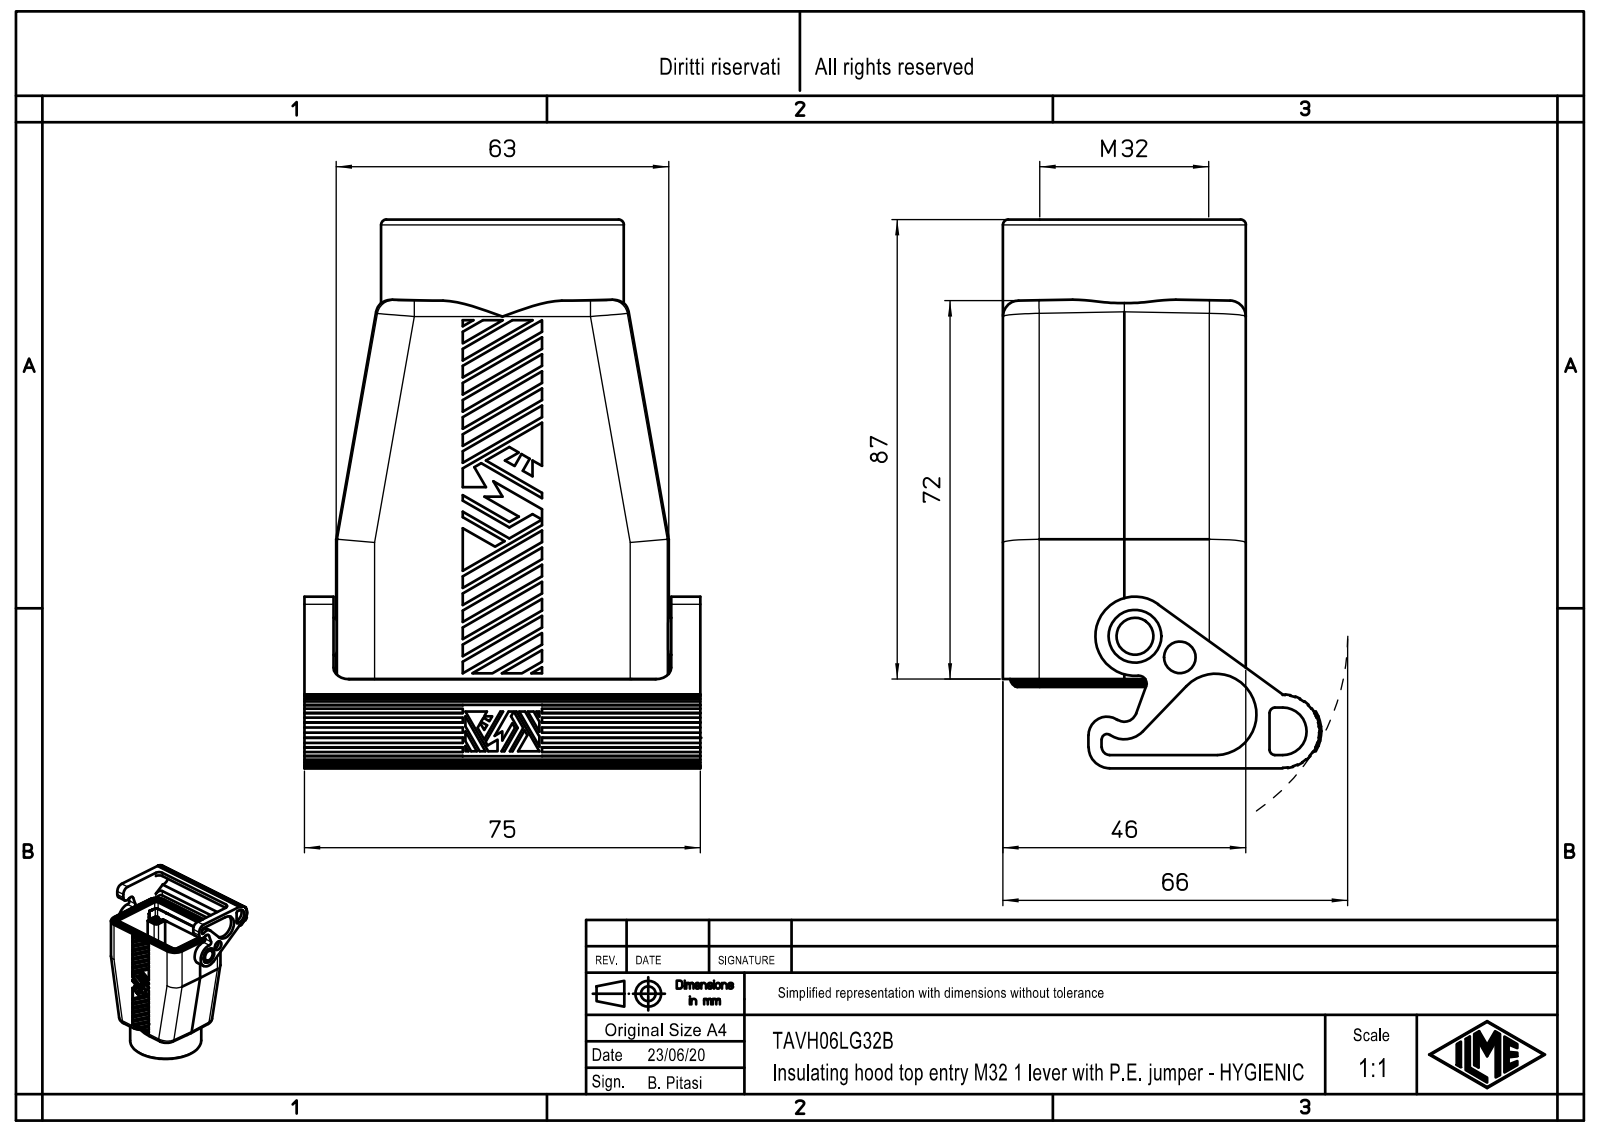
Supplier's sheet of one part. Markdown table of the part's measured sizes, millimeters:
| quantity | value |
| --- | --- |
| part name | TAVH06LG32B |
| STEP written by | Creo Elements/Direct Modeling 20.1B 02-Apr-2019 (C) Parametric Technology GmbH (AUTOMOTIVE_DESIGN) |
| units | millimeters |
| bodies | 1 solid, 680 faces (490 planar, 162 cylindrical, 28 other) |
| overall size | 103.9 × 75 × 60.3 |
| volume | 108 466 mm³ |
| surface area | 45 556 mm² |
| round holes (diameter × count) | 3.5 × 4, 5.12 × 4, 6.5 × 4, 6 × 1, 10 × 1, 28 × 1, 32 × 1 |
| round bosses / shafts (diameter × count) | 46 × 1, 7 × 1 |
| partial cylindrical surfaces (radius × count) | 1.5 × 14, 7 × 9, 1.81 × 8, 2 × 8, 3 × 8, 1 × 6, 1.3 × 4, 1.6 × 4 |
| main face-to-face distances | 46, 0.5, 7.98, 45.5, 5.5, 3, 69.5, 5.6, 2.5, 8 |
| hole center spacings | 25.81, 27, 44, 51.62, 9.39 |
